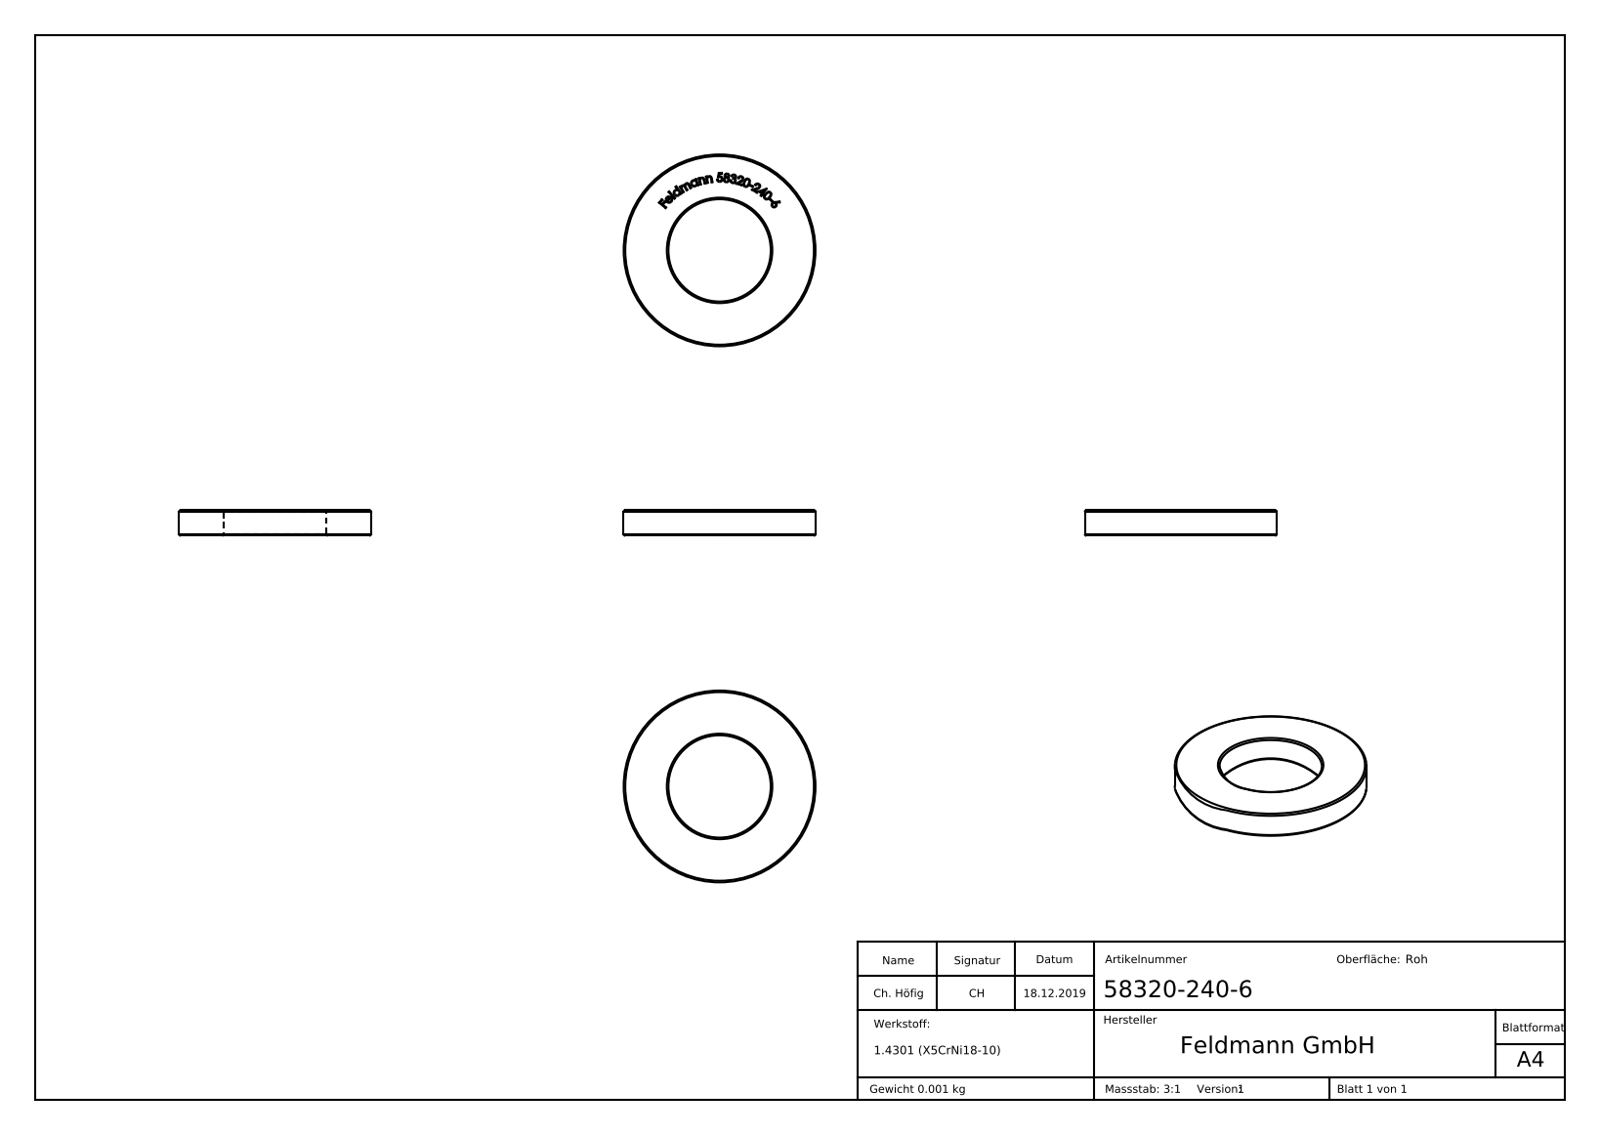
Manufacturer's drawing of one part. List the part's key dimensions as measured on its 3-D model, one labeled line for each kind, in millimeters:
Part name (STEP PRODUCT): 58320-240-6
STEP written by: SolidWorks 2015 (CONFIG_CONTROL_DESIGN)
Units: millimetres
Bodies: 1 solid, 261 faces (129 planar, 2 cylindrical, 130 other)
Overall size (bounding box): 12 × 12 × 1.6
Volume: 129 mm³ · Surface area: 254 mm²
Round holes (diameter × count): ⌀6.4 ×1
Round bosses / shafts (diameter × count): ⌀12 ×1
Main face-to-face distances: 1.6, 1.5, 0.34, 0.53, 0.39, 0.48, 0.58, 0.31, 0.32, 0.54
